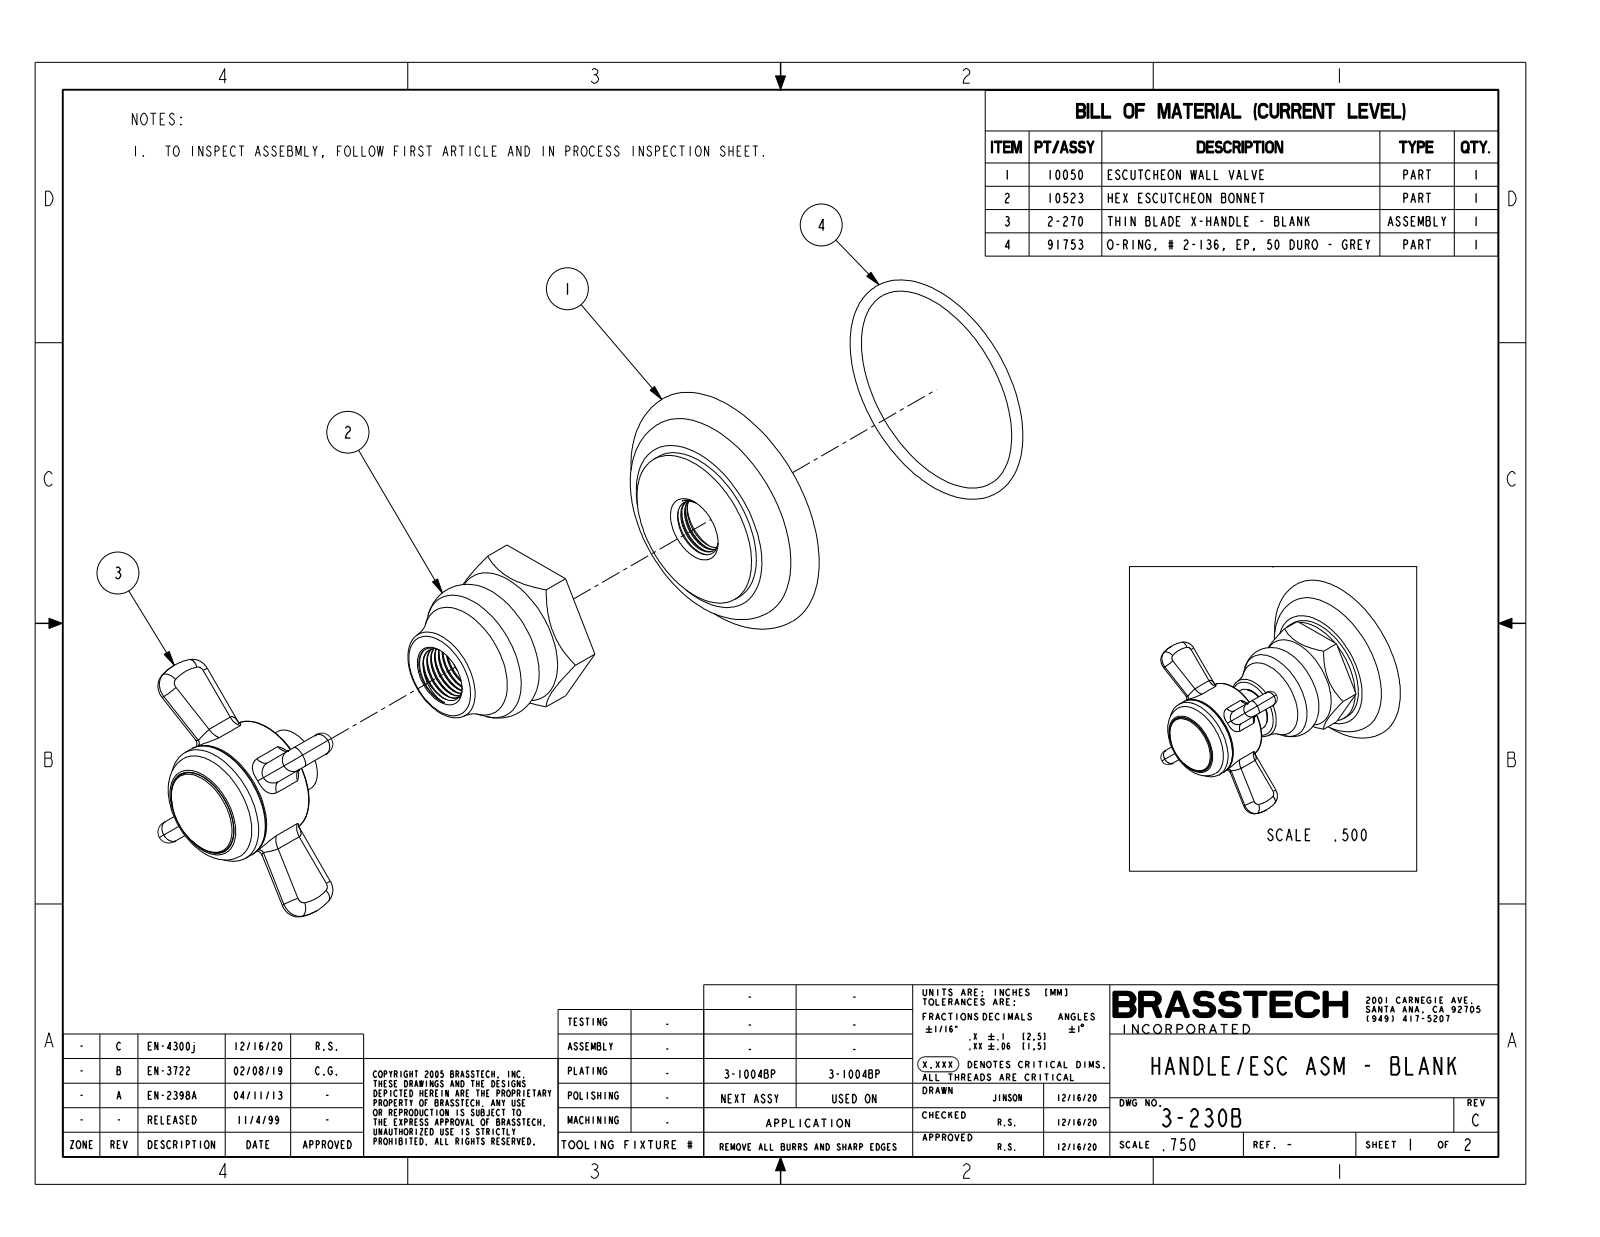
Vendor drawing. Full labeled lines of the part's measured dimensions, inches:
Part name (STEP PRODUCT): 3-230B
STEP written by: CREO PARAMETRIC BY PTC INC, 2018400 (CONFIG_CONTROL_DESIGN)
Units: inches
Bodies: 1 solid, 155 faces (33 planar, 30 cylindrical, 92 other)
Overall size (bounding box): 3.047 × 2.36 × 2.36
Volume: 4.013 in³ · Surface area: 23.94 in²
Round holes (diameter × count): ⌀0.815 ×1
Round bosses / shafts (diameter × count): ⌀1.482 ×1, ⌀1.115 ×1, ⌀1.1 ×1, ⌀0.8 ×1, ⌀0.603 ×1, ⌀0.4 ×1
Partial cylindrical surfaces — rounded edges, fillets, slot ends (radius × count): R0.1 ×14
Main face-to-face distances: 0.2, 2.057, 1.313, 1.687, 0.37, 0.375, 1.312, 1.682, 2.777, 2.402
